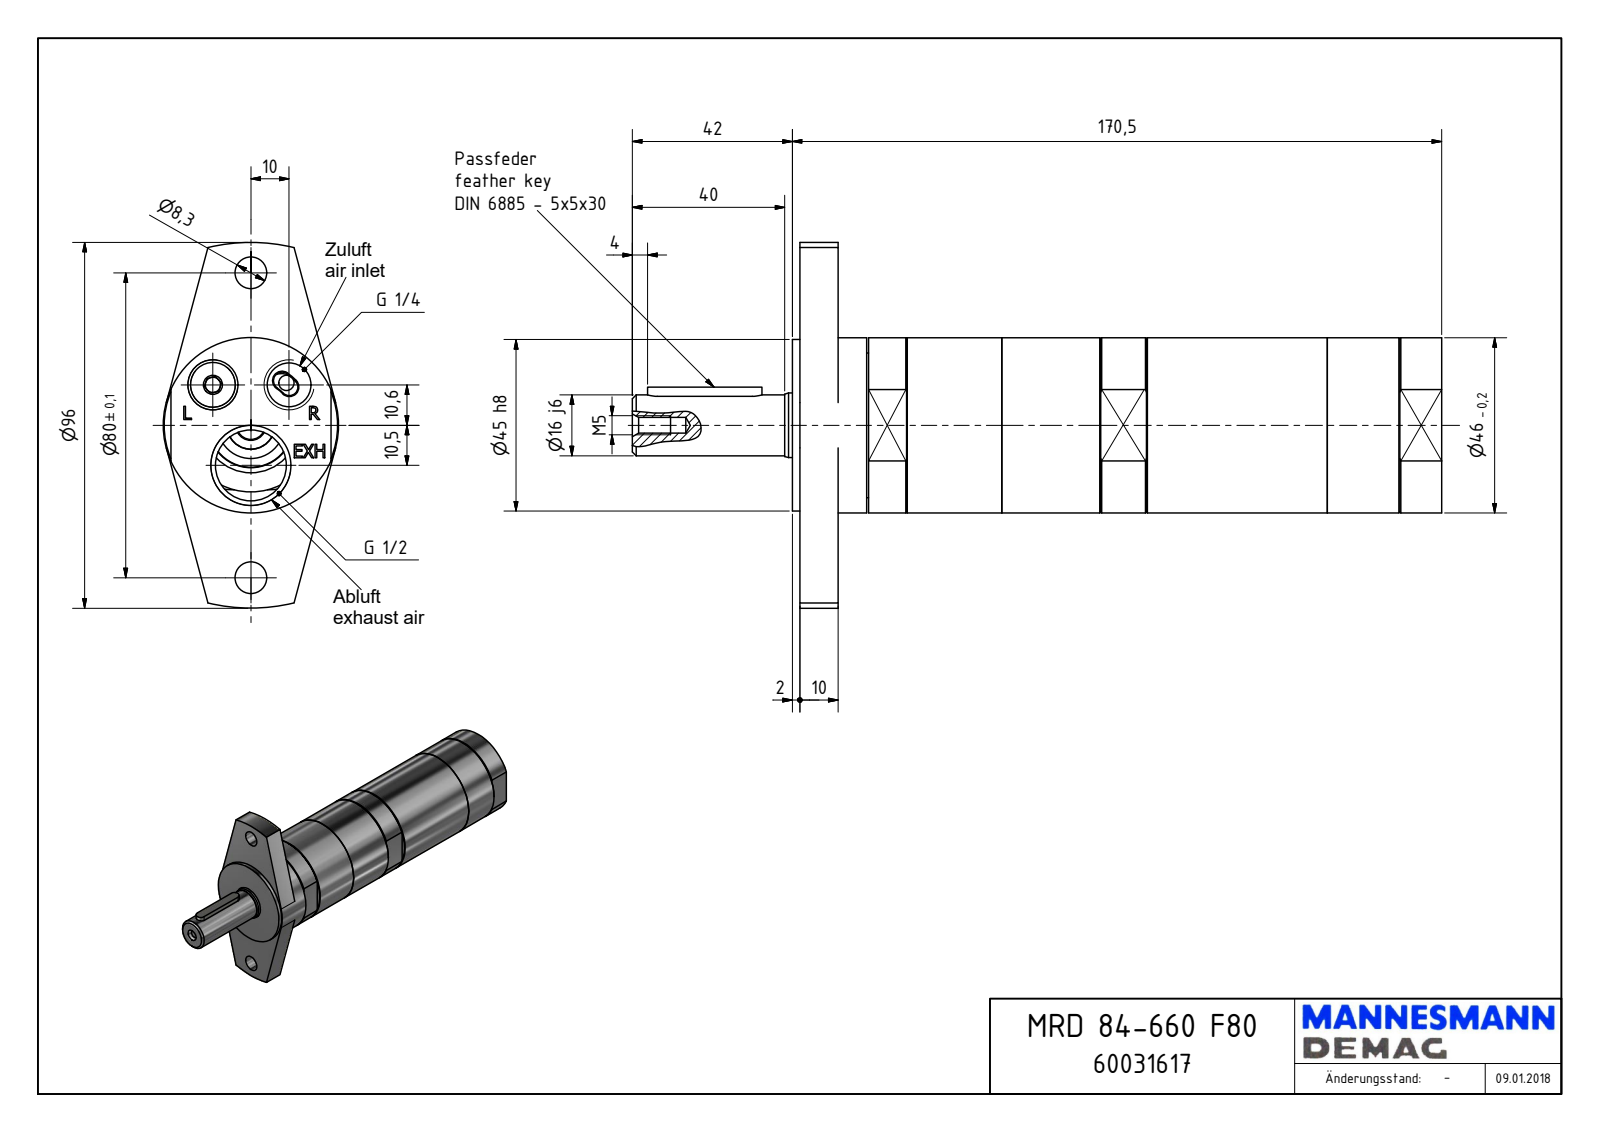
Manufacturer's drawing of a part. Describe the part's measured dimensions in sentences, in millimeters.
The part is named "MRD 84-660 F80_60031317". Its 3-D file was written by "Autodesk Inventor 2018 (AUTOMOTIVE_DESIGN)". It is 1 solid with 185 faces: 116 planar, 38 cylindrical and 31 other. Overall it measures 212.5 by 96 by 46 millimeters. Its volume is 301 404 cubic millimeters and its surface area 39 612 square millimeters. Round holes: 2 of diameter 8.3, 1 of diameter 4, 1 of diameter 4.13, 1 of diameter 11.45, 1 of diameter 17.5, 1 of diameter 18.63, 1 of diameter 38, 1 of diameter 38.38, 1 of diameter 42. Round bosses or shafts: 1 of diameter 46, 1 of diameter 45, 1 of diameter 41.3, 1 of diameter 16.95, 1 of diameter 16. Partial cylindrical surfaces (rounded edges, fillets, slot ends): 2 of radius 2.5, 2 of radius 5, 1 of radius 5.72, 1 of radius 17.3, 1 of radius 48. The main face-to-face distances are 10, 12, 2, 158.5, 170.5, 168.5, 42, 150.5, 8, 18. The hole center spacings are 14.57, 23.35, 31.05, 40, 51.58, 10.5, 20, 29.5.
